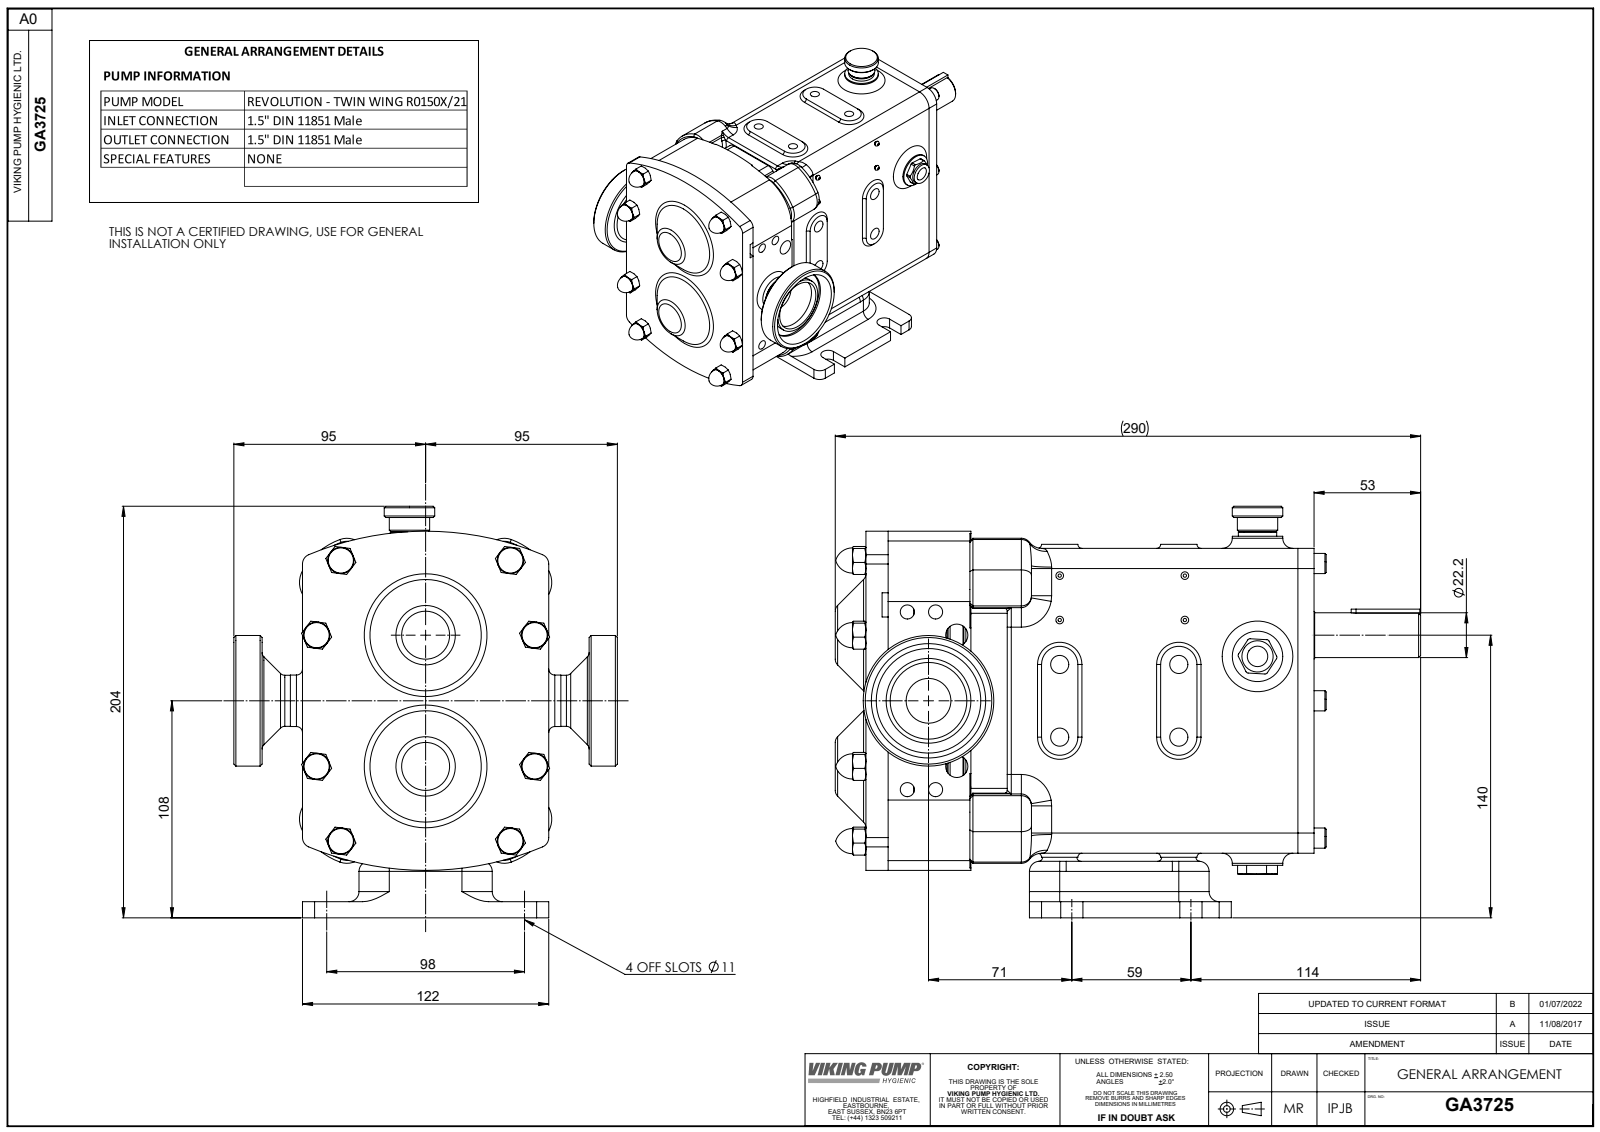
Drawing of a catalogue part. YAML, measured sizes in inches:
part_name: "Copy of R0150 CPP H TSD^GA3725; Copy of Z94-5031-12 - 1INCH TO 1.5 INCH DIN11851^GA3725; GA3725"
step_written_by: "SolidWorks 2023 (AUTOMOTIVE_DESIGN)"
units: inches
bodies: {solids: 3, faces: 1259, planar: 369, cylindrical: 341, other: 549}
overall_size: [11.417, 8.026, 7.48]
volume: 213.1
surface_area: 384.3
round_holes:
  - {diameter: 0.268, count: 4}
  - {diameter: 0.276, count: 4}
  - {diameter: 0.354, count: 4}
  - {diameter: 0.433, count: 2}
  - {diameter: 0.874, count: 1}
  - {diameter: 0.887, count: 1}
  - {diameter: 1.496, count: 1}
  - {diameter: 2.039, count: 1}
round_bosses_or_shafts:
  - {diameter: 0.394, count: 6}
  - {diameter: 0.984, count: 4}
  - {diameter: 0.512, count: 4}
  - {diameter: 2.547, count: 1}
  - {diameter: 1.654, count: 1}
  - {diameter: 1.004, count: 1}
  - {diameter: 0.996, count: 1}
  - {diameter: 0.985, count: 1}
partial_cylinders:
  - {radius: 0.079, count: 28}
  - {radius: 0.394, count: 26}
  - {radius: 0.197, count: 19}
  - {radius: 0.236, count: 14}
  - {radius: 0.315, count: 8}
  - {radius: 0.05, count: 6}
  - {radius: 1.22, count: 6}
  - {radius: 0.049, count: 4}
face_to_face_distances: [3.386, 0.709, 8.74, 4.094, 0.236, 0.079, 7.205, 0.787, 5.945, 2.047]
hole_center_spacings: [1.417, 2.323, 2.721, 0.551, 0.613, 1.065, 1.393, 1.738]
